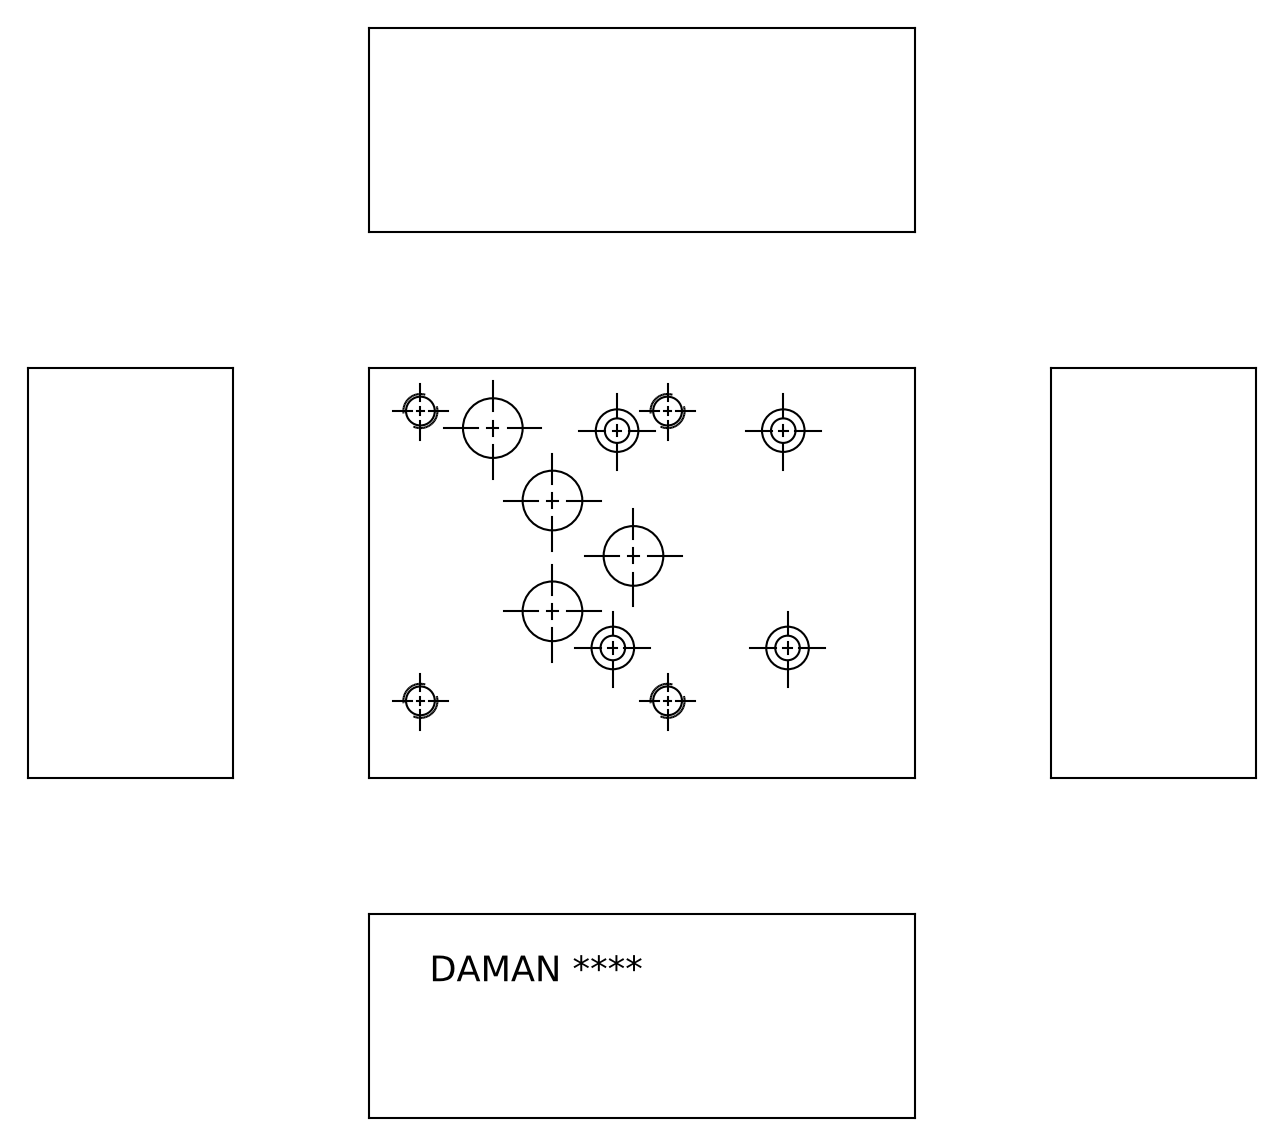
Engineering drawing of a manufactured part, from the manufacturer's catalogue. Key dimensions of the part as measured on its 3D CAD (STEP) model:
Part name (STEP PRODUCT): Part_AD05D03VAABA.B00171R5_3D
STEP written by: Autodesk Inventor 2022 (AUTOMOTIVE_DESIGN)
Units: millimetres
Bodies: 1 solid, 407 faces (267 planar, 31 cylindrical, 109 other)
Overall size (bounding box): 101.6 × 76.2 × 38.1
Volume: 285 679 mm³ · Surface area: 33 984 mm²
Round holes (diameter × count): ⌀6.35 ×8, ⌀5.11 ×4, ⌀5.54 ×4, ⌀8.74 ×4, ⌀11.13 ×4, ⌀12.7 ×4, ⌀3.17 ×1
Partial cylindrical surfaces — rounded edges, fillets, slot ends (radius × count): R2.77 ×2
Main face-to-face distances: 38.1, 76.2, 101.6, 1.32, 36.78, 30.96, 29.64, 7.14, 76.16, 5.56
Hole centre spacings: 22.04, 40.49, 51.45, 2.77, 7.49, 10.19, 10.38, 11.1
